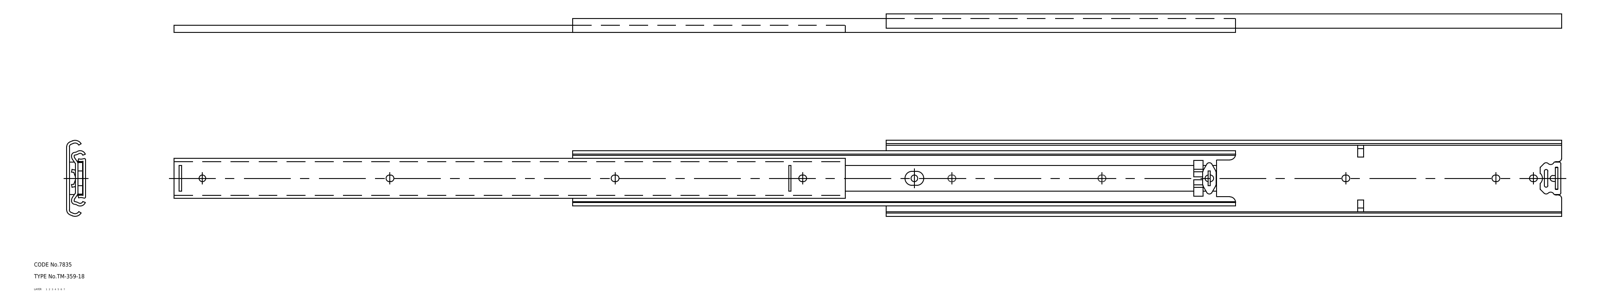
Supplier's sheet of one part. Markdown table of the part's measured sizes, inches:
| quantity | value |
| --- | --- |
| part name | member_C; member_B; member_A; TM_359_18 |
| STEP written by | SolidWorks 2015 (AUTOMOTIVE_DESIGN) |
| units | inches |
| bodies | 3 solids, 233 faces (128 planar, 105 cylindrical, 0 other) |
| overall size | 36.976 × 2.028 × 0.504 |
| volume | 7.326 in³ |
| surface area | 217.4 in² |
| round holes (diameter × count) | 0.177 × 3 |
| partial cylindrical surfaces (radius × count) | 0.089 × 16, 0.079 × 11, 0.187 × 6, 0.018 × 4, 0.02 × 4, 0.024 × 4, 0.012 × 2, 0.03 × 2 |
| main face-to-face distances | 0.071, 0.233, 0.5, 0.429, 0.366, 0.437, 0.063, 0.162, 0.204, 0.267 |
| hole center spacings | 8.118, 10.858, 18.976 |
